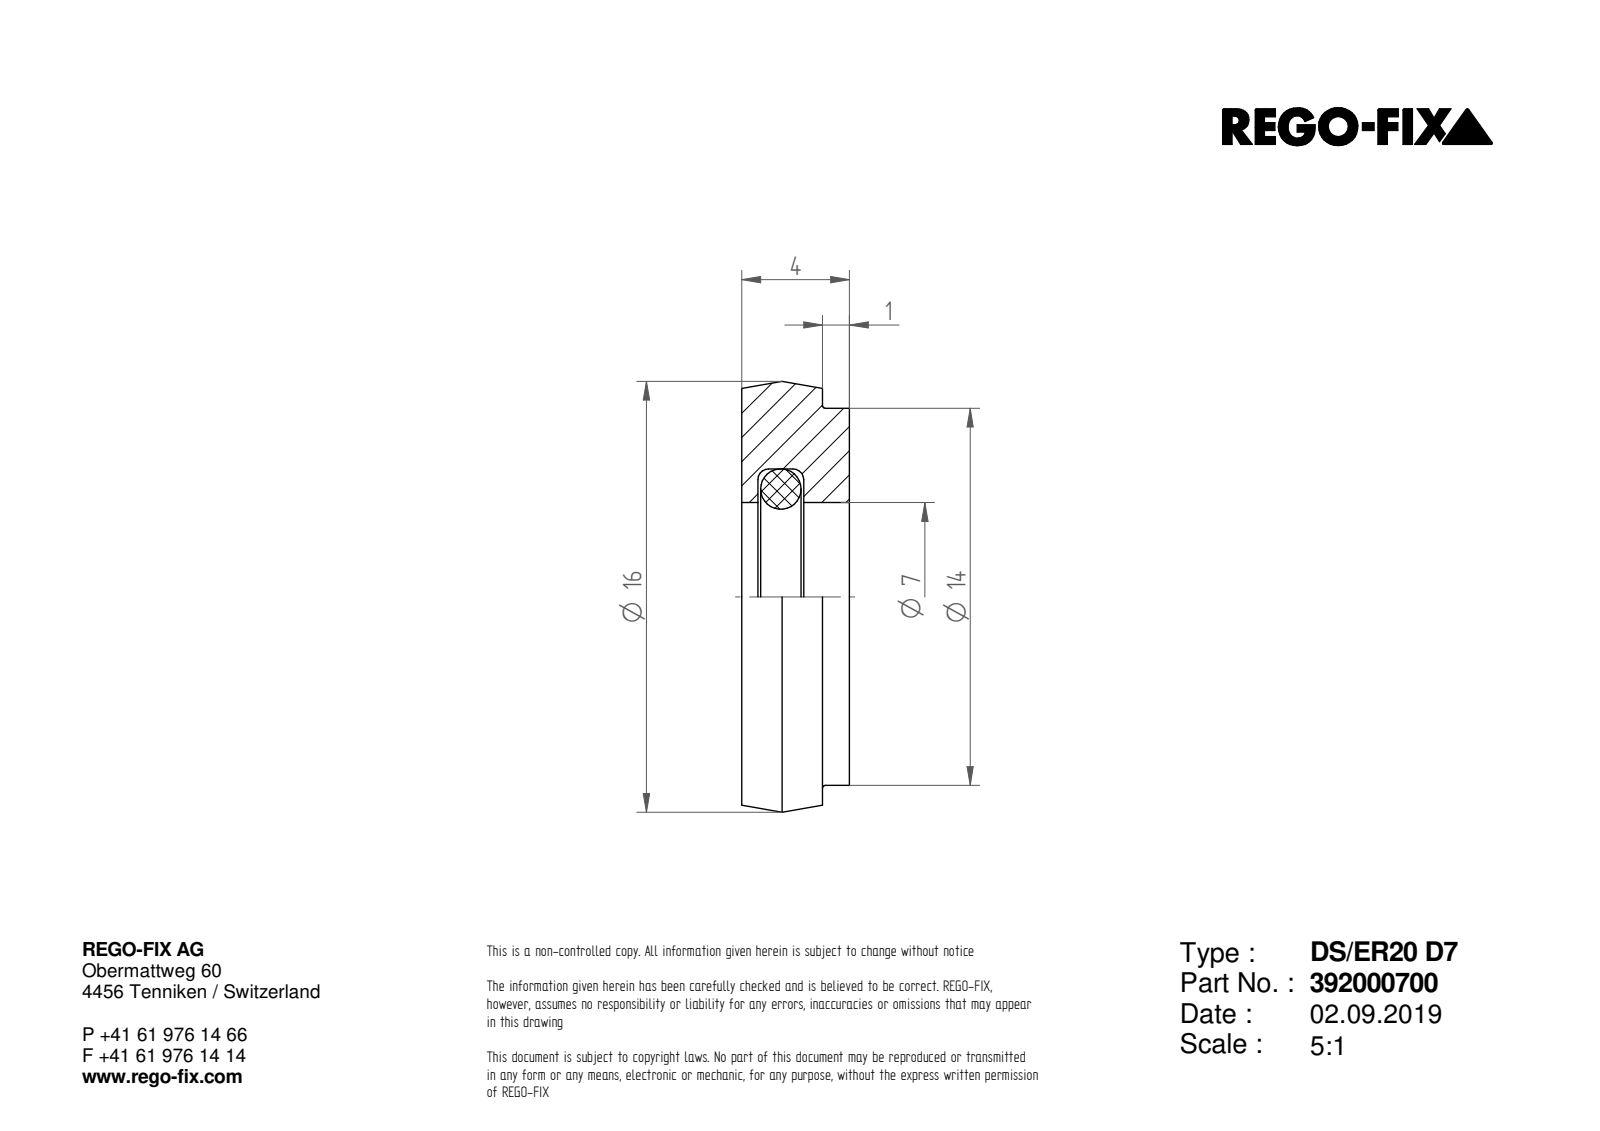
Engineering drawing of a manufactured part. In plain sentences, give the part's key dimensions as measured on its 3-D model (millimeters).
The part is named "NOCUT". Its 3-D file was written by "SIEMENS PLM Software Solid Edge ST10 (AUTOMOTIVE_DESIGN)". It is 1 solid with 7 faces: 3 planar, 3 cylindrical and 1 other. Overall it measures 16 by 16 by 4 millimeters. Its volume is 603 cubic millimeters and its surface area 606 square millimeters. Round holes: 1 of diameter 7. Round bosses or shafts: 1 of diameter 16, 1 of diameter 14. The main face-to-face distances are 4, 1, 3.
